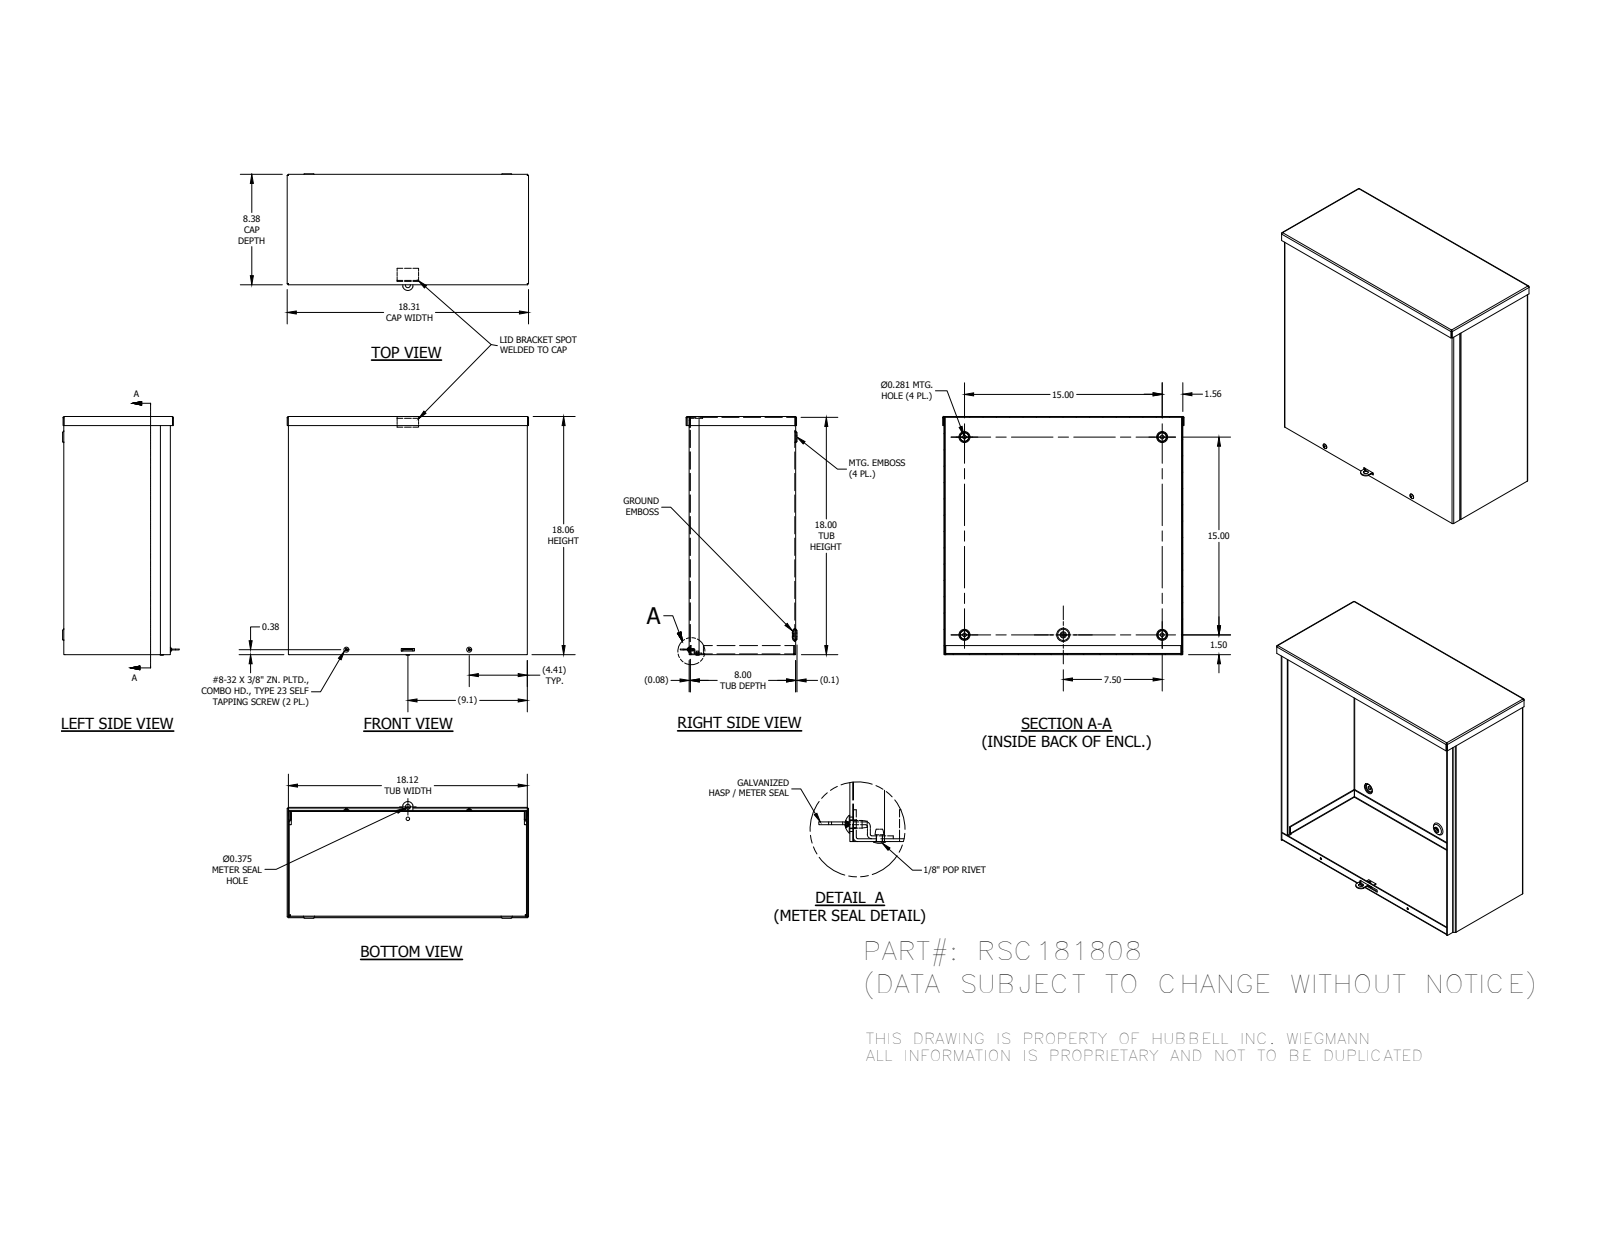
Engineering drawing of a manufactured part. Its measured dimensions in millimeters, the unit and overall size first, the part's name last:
Units: millimetres
Overall size (bounding box): 465.11 × 459.79 × 224.8
Round holes (diameter × count): ⌀7.14 ×4, ⌀7.94 ×4, ⌀3.73 ×2, ⌀3.17 ×1, ⌀3.45 ×1, ⌀4.34 ×1, ⌀9.52 ×1
Round bosses / shafts (diameter × count): ⌀9.75 ×2, ⌀4.17 ×2, ⌀6.65 ×1, ⌀5.93 ×1, ⌀3.17 ×1
Partial cylindrical surfaces — rounded edges, fillets, slot ends (radius × count): R0.79 ×19, R2.37 ×18, R2.67 ×1, R10.16 ×1
Main face-to-face distances: 1.57, 203.6, 457.2, 458.77, 205.17, 202.03, 455.63, 460.34, 1.58, 203.2
Hole centre spacings: 77.68, 310.09, 236.54, 121.67, 381, 415.9, 512.93, 190.5
Volume: 1 346 000 mm³ · Surface area: 1 722 000 mm²
Bodies: 9 solids, 320 faces (183 planar, 61 cylindrical, 76 other)
Part name (STEP PRODUCT): RSC181808BKPA; RSC1808EWPA-16GA; RSC1818LFA; RSC1808CPA-16GA (+5 more)
STEP written by: Autodesk Inventor 2014 (AUTOMOTIVE_DESIGN)
